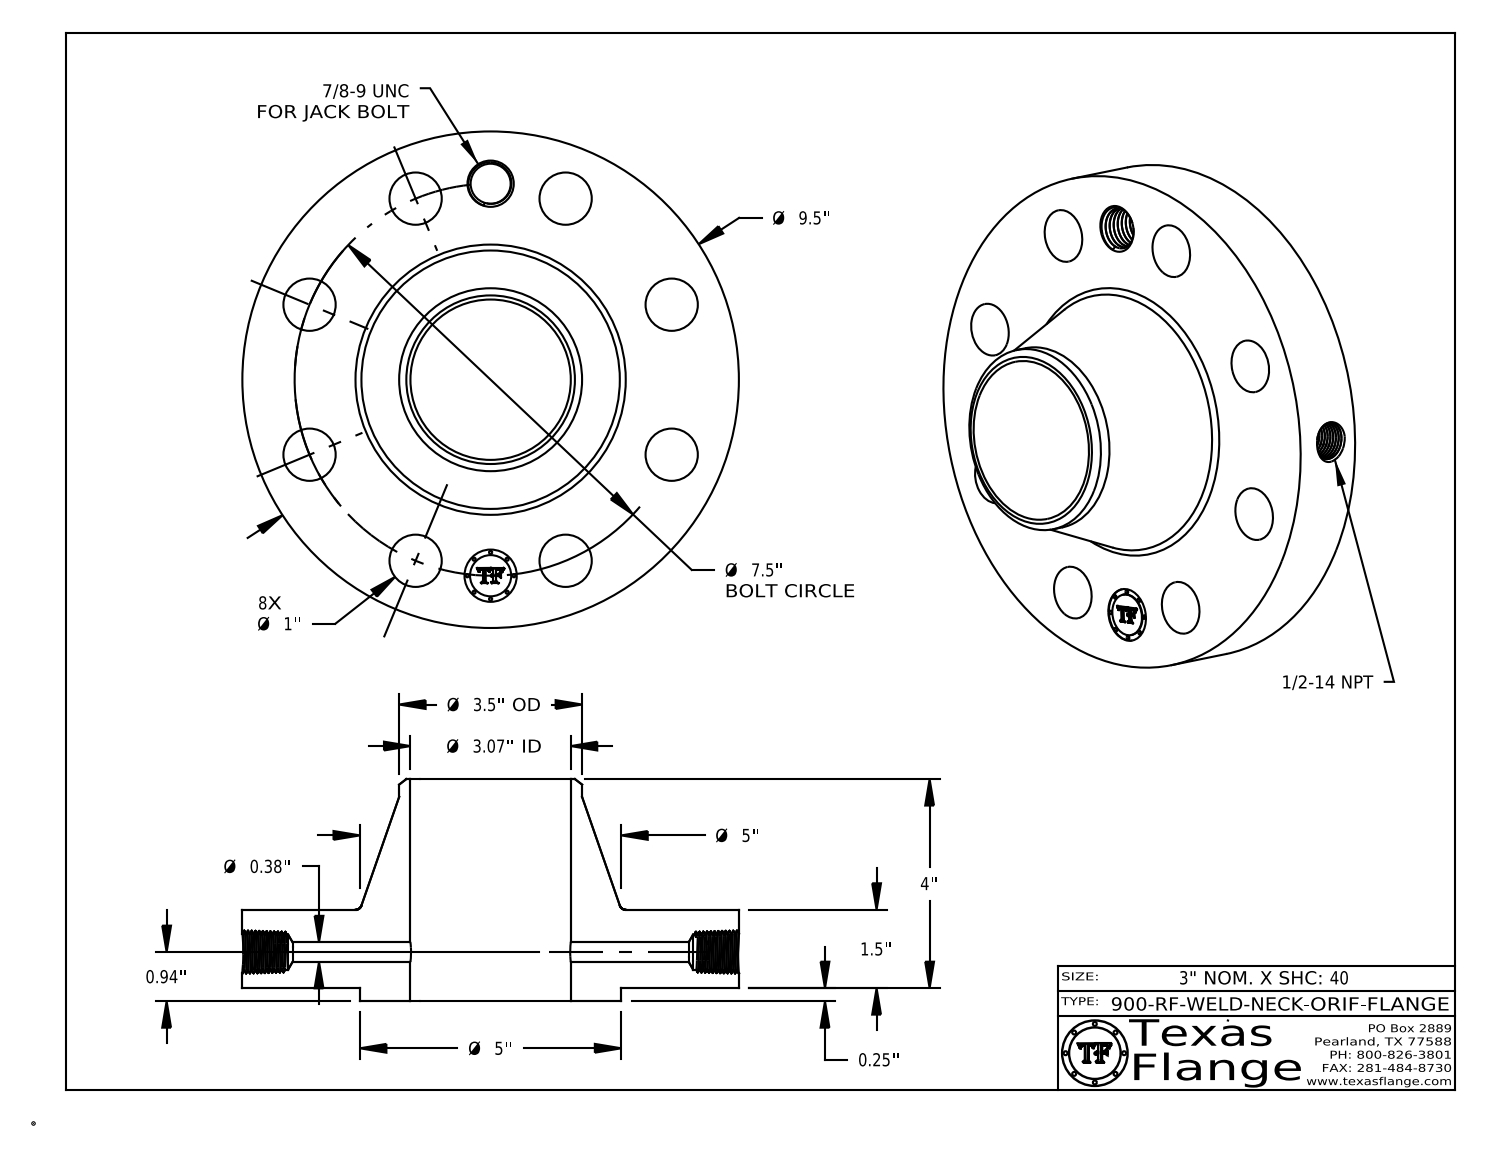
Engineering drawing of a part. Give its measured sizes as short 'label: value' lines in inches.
name: 900-RF-WELD-NECK
written by: CATIA V5 STEP AP214 (AUTOMOTIVE_DESIGN)
unit: in
bodies: 1 solid, 759 faces (369 planar, 90 cylindrical, 300 other)
size: 9.5 × 9.5 × 4.25
volume: 102.5 in³; area: 281.3 in²
holes: 9× ⌀1, 1× ⌀0.375, 1× ⌀0.672, 1× ⌀0.766, 1× ⌀3.068
bosses: 8× ⌀0.061, 1× ⌀9.5, 1× ⌀5, 1× ⌀3.5, 1× ⌀0.788
face distances: 1.5, 0.25, 1.75, 4.25, 4, 2.5, 1.735, 1.485, 0.015, 2.515
hole spacings: 3.75, 2.87, 5.303, 6.929, 7.5, 1.463, 4.167, 6.236
